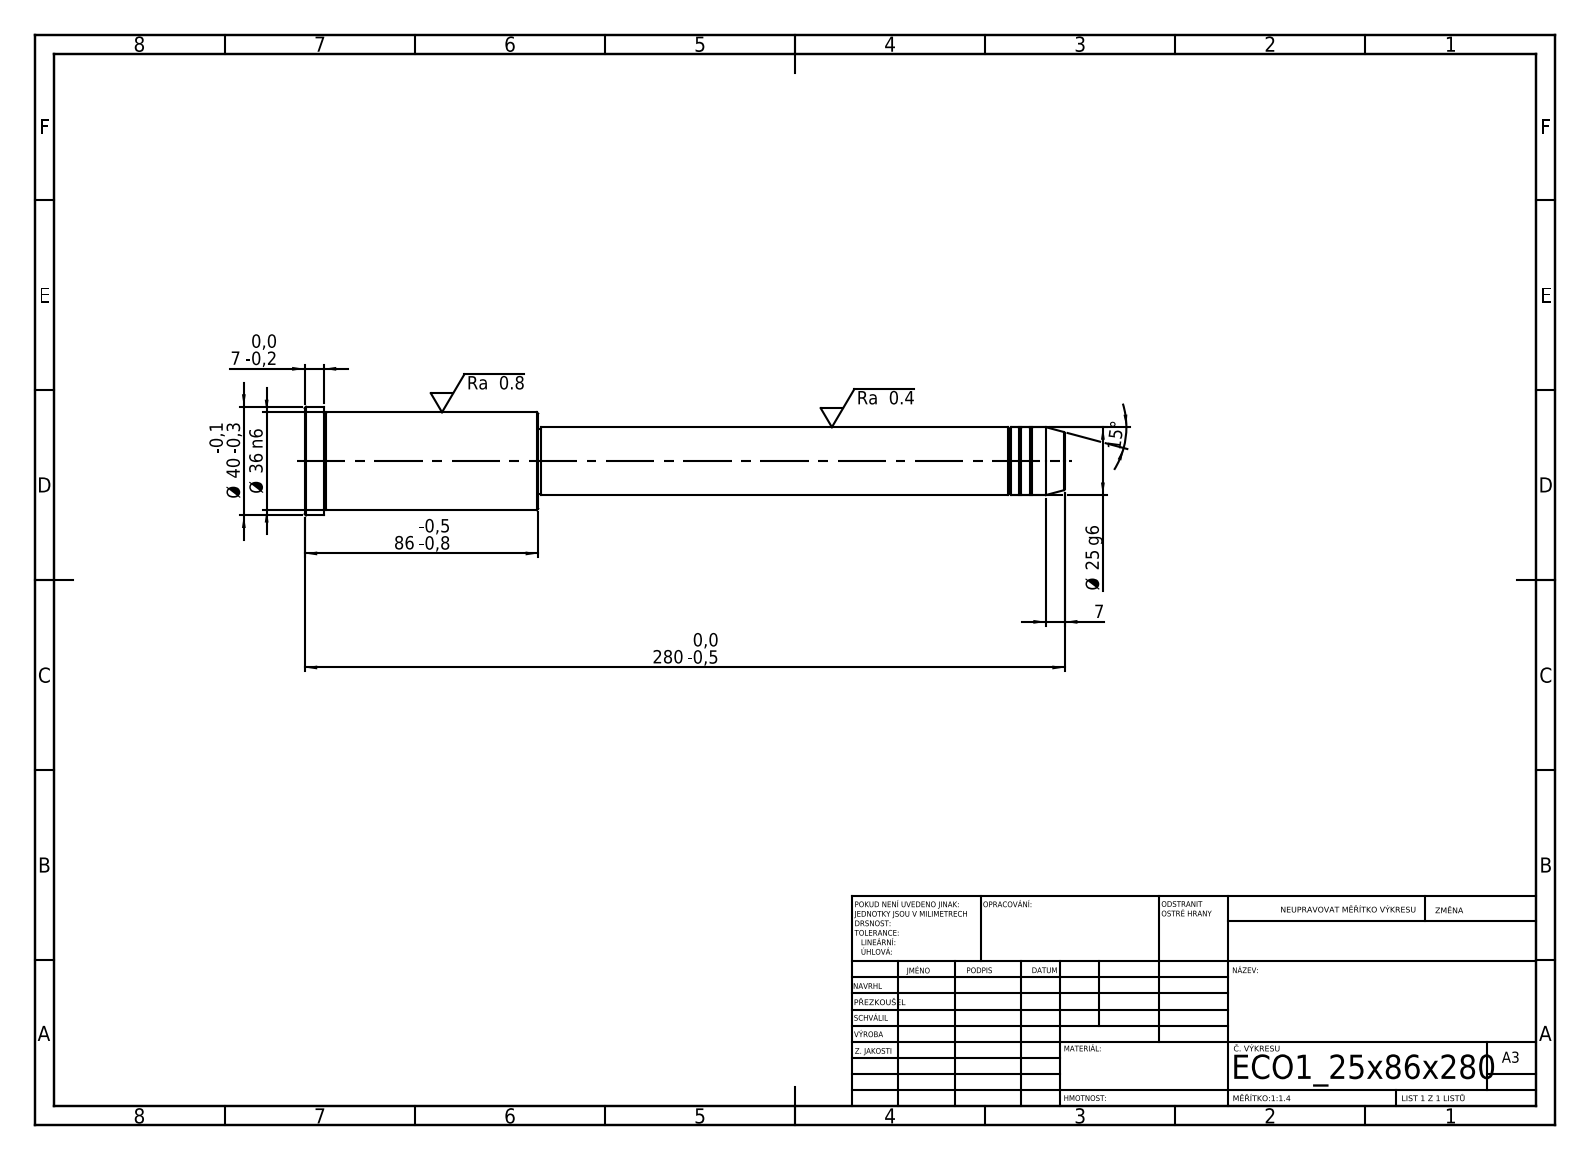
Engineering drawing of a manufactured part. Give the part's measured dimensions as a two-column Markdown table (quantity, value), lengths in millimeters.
| quantity | value |
| --- | --- |
| STEP written by | SolidWorks 2019 (CONFIG_CONTROL_DESIGN) |
| units | millimeters |
| bodies | 1 solid, 43 faces (5 planar, 14 cylindrical, 24 other) |
| overall size | 280 × 40 × 40 |
| volume | 183 744 mm³ |
| surface area | 27 587 mm² |
| round bosses / shafts (diameter × count) | 40 × 1, 36 × 1, 25 × 1, 24 × 1 |
| main face-to-face distances | 86, 194, 280, 273, 79, 7, 193, 1, 80, 87 |
